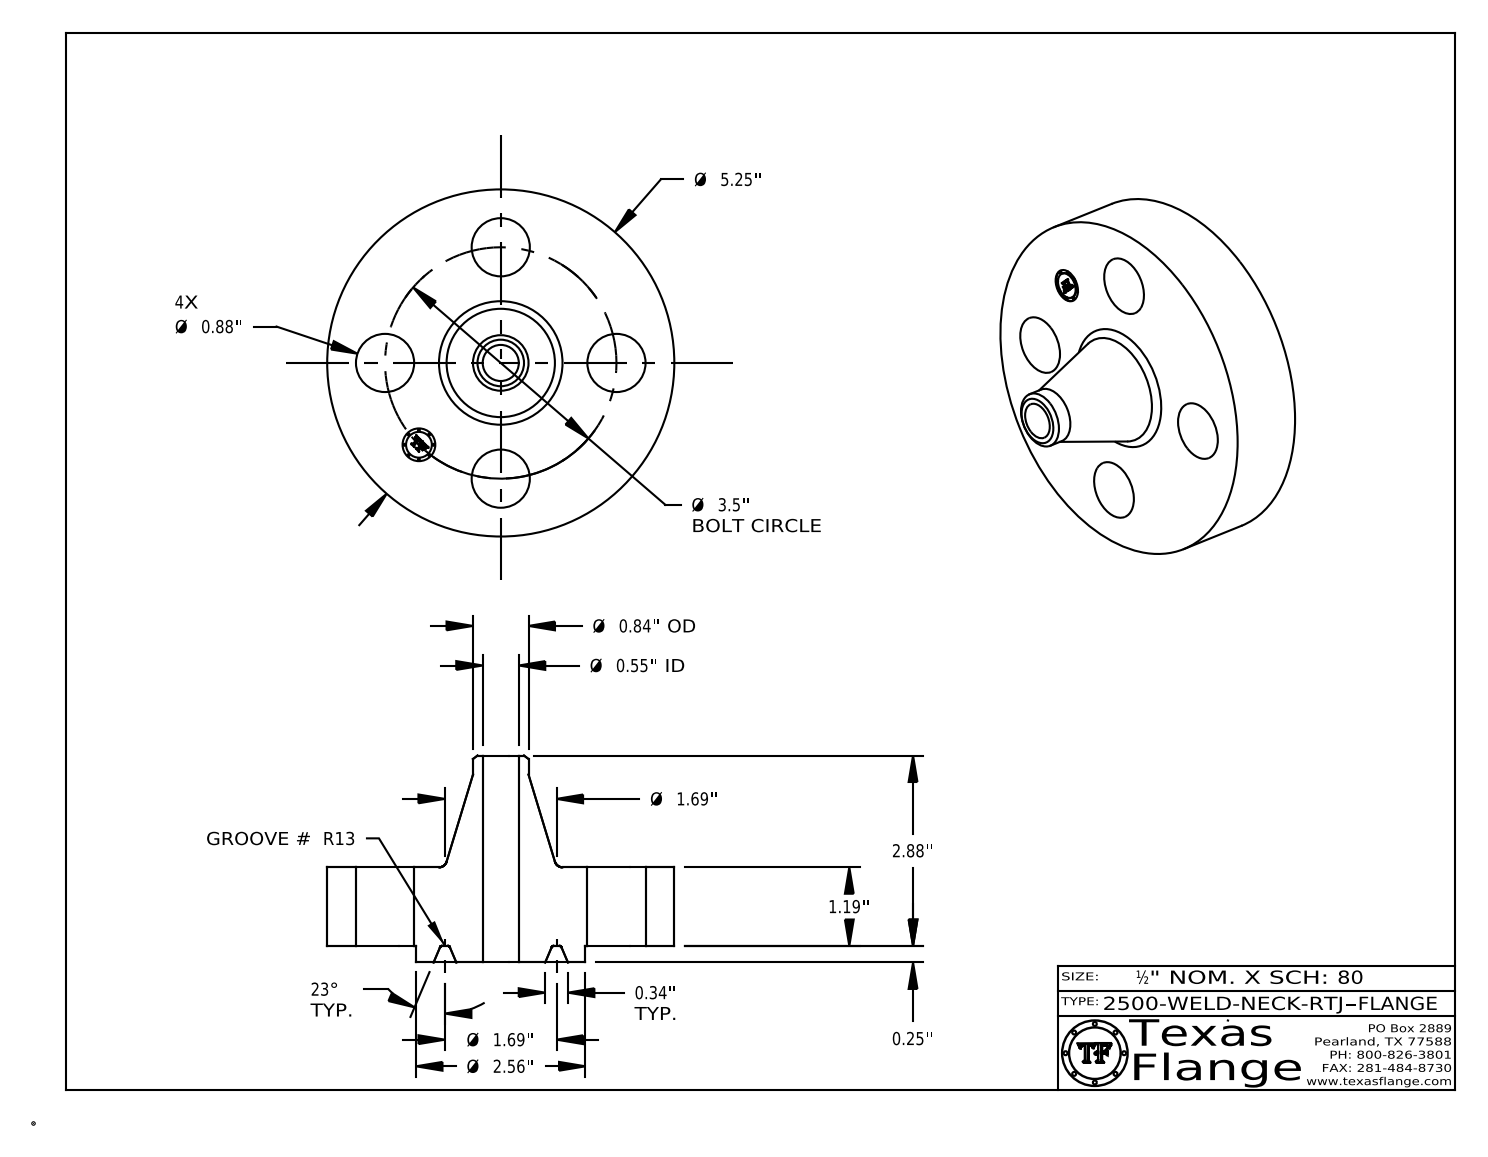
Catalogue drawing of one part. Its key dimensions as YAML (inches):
part_name: "2500-WELD-NECK-RTJ"
step_written_by: "CATIA V5 STEP AP214 (AUTOMOTIVE_DESIGN)"
units: inches
bodies: {solids: 1, faces: 421, planar: 371, cylindrical: 36, other: 14}
overall_size: [5.25, 5.25, 3.13]
volume: 25.1
surface_area: 84.6
round_holes:
  - {diameter: 0.88, count: 4}
  - {diameter: 0.495, count: 1}
  - {diameter: 0.546, count: 1}
round_bosses_or_shafts:
  - {diameter: 0.03, count: 8}
  - {diameter: 5.25, count: 1}
  - {diameter: 2.563, count: 1}
  - {diameter: 0.84, count: 1}
  - {diameter: 0.39, count: 1}
face_to_face_distances: [1.19, 0.25, 1.44, 3.13, 2.88, 1.69, 1.425, 1.175, 0.015, 1.705]
hole_center_spacings: [1.75, 2.475, 1.339, 3.233, 3.5]
